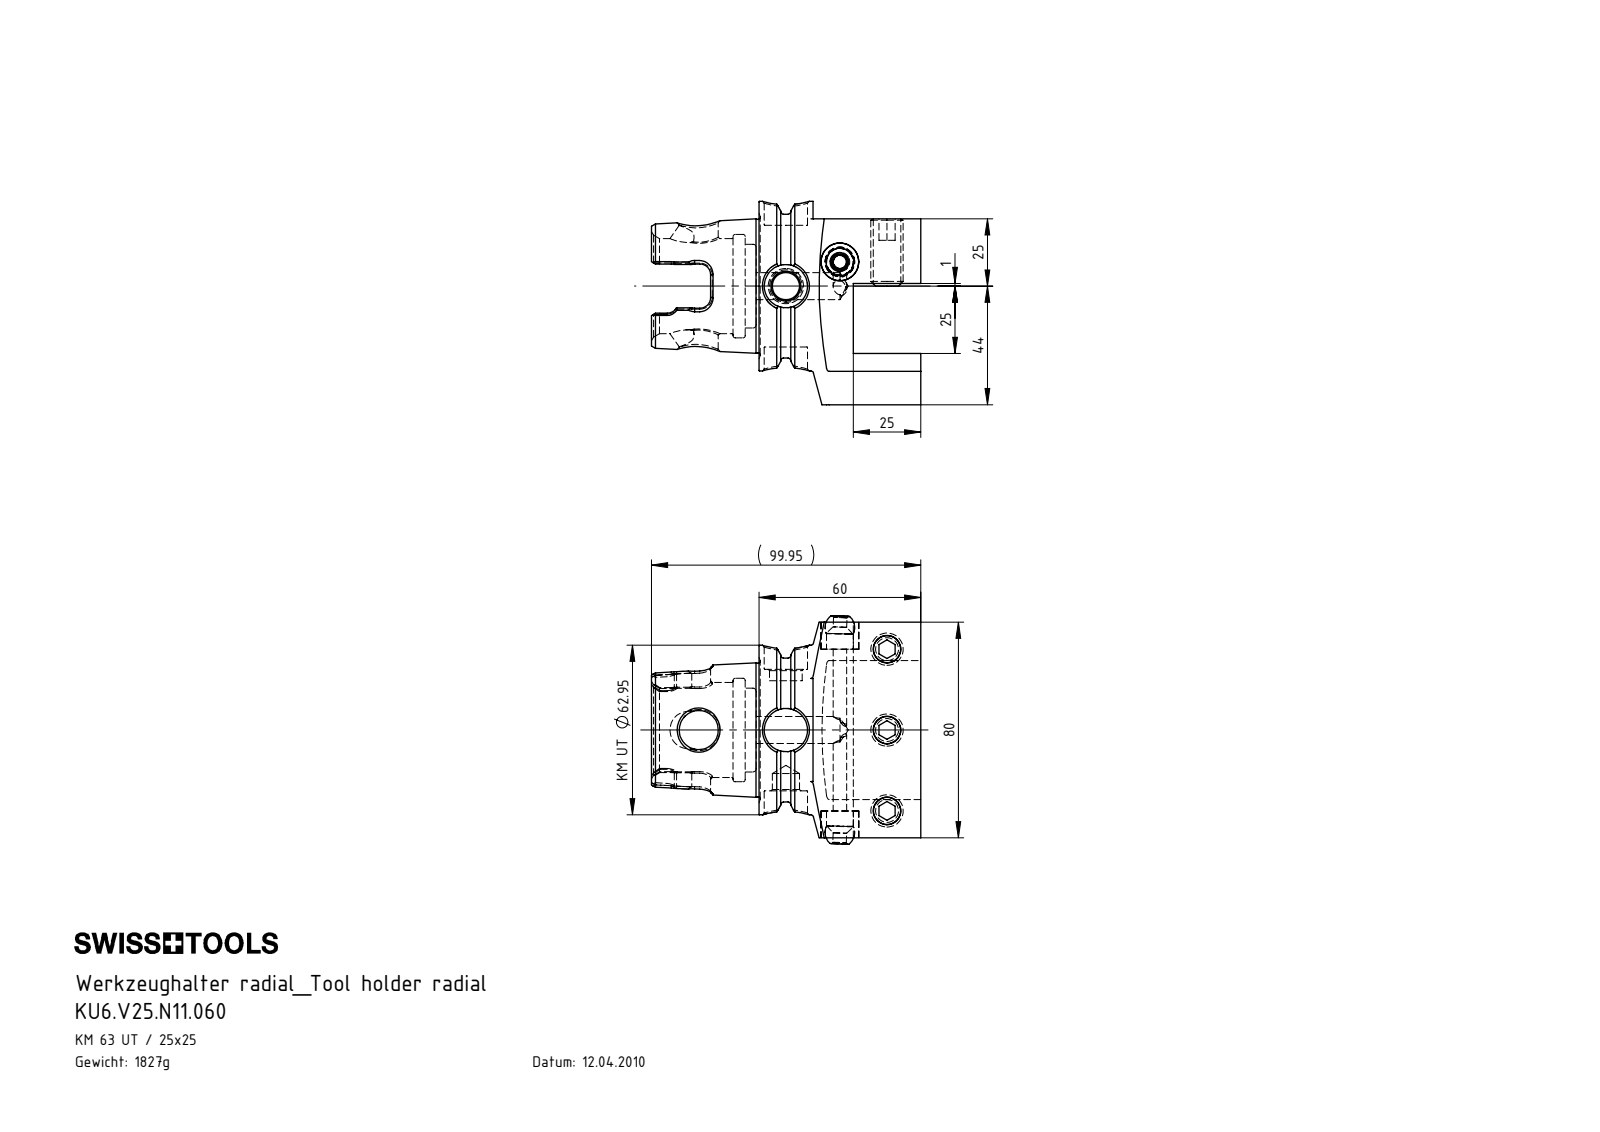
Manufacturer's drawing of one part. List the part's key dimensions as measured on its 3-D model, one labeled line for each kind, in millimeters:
Part name (STEP PRODUCT): ISO 4026 - M12 x 25; KU6-V25.N11.060_A; KU6.V25.N11.060; KU1-U14.001.012_1 (+2 more)
STEP written by: SolidWorks 2022 (AUTOMOTIVE_DESIGN)
Units: millimetres
Bodies: 8 solids, 336 faces (94 planar, 82 cylindrical, 160 other)
Overall size (bounding box): 99.95 × 85.63 × 75.47
Volume: 233 888 mm³ · Surface area: 50 244 mm²
Round holes (diameter × count): ⌀5 ×4, ⌀10.2 ×3, ⌀10 ×2, ⌀16.05 ×2, ⌀10.1 ×1, ⌀12.1 ×1, ⌀14 ×1, ⌀14.5 ×1, ⌀31.1 ×1, ⌀35.27 ×1, ⌀38.4 ×1
Round bosses / shafts (diameter × count): ⌀12 ×3, ⌀62.95 ×1
Partial cylindrical surfaces — rounded edges, fillets, slot ends (radius × count): R4 ×6, R7.04 ×2, R27.85 ×1, R51 ×1
Main face-to-face distances: 25, 50, 19, 69, 45, 26, 24, 80, 60, 35
Hole centre spacings: 30, 48.06, 76.07, 21.98, 32.35, 37.55, 60, 69.9
